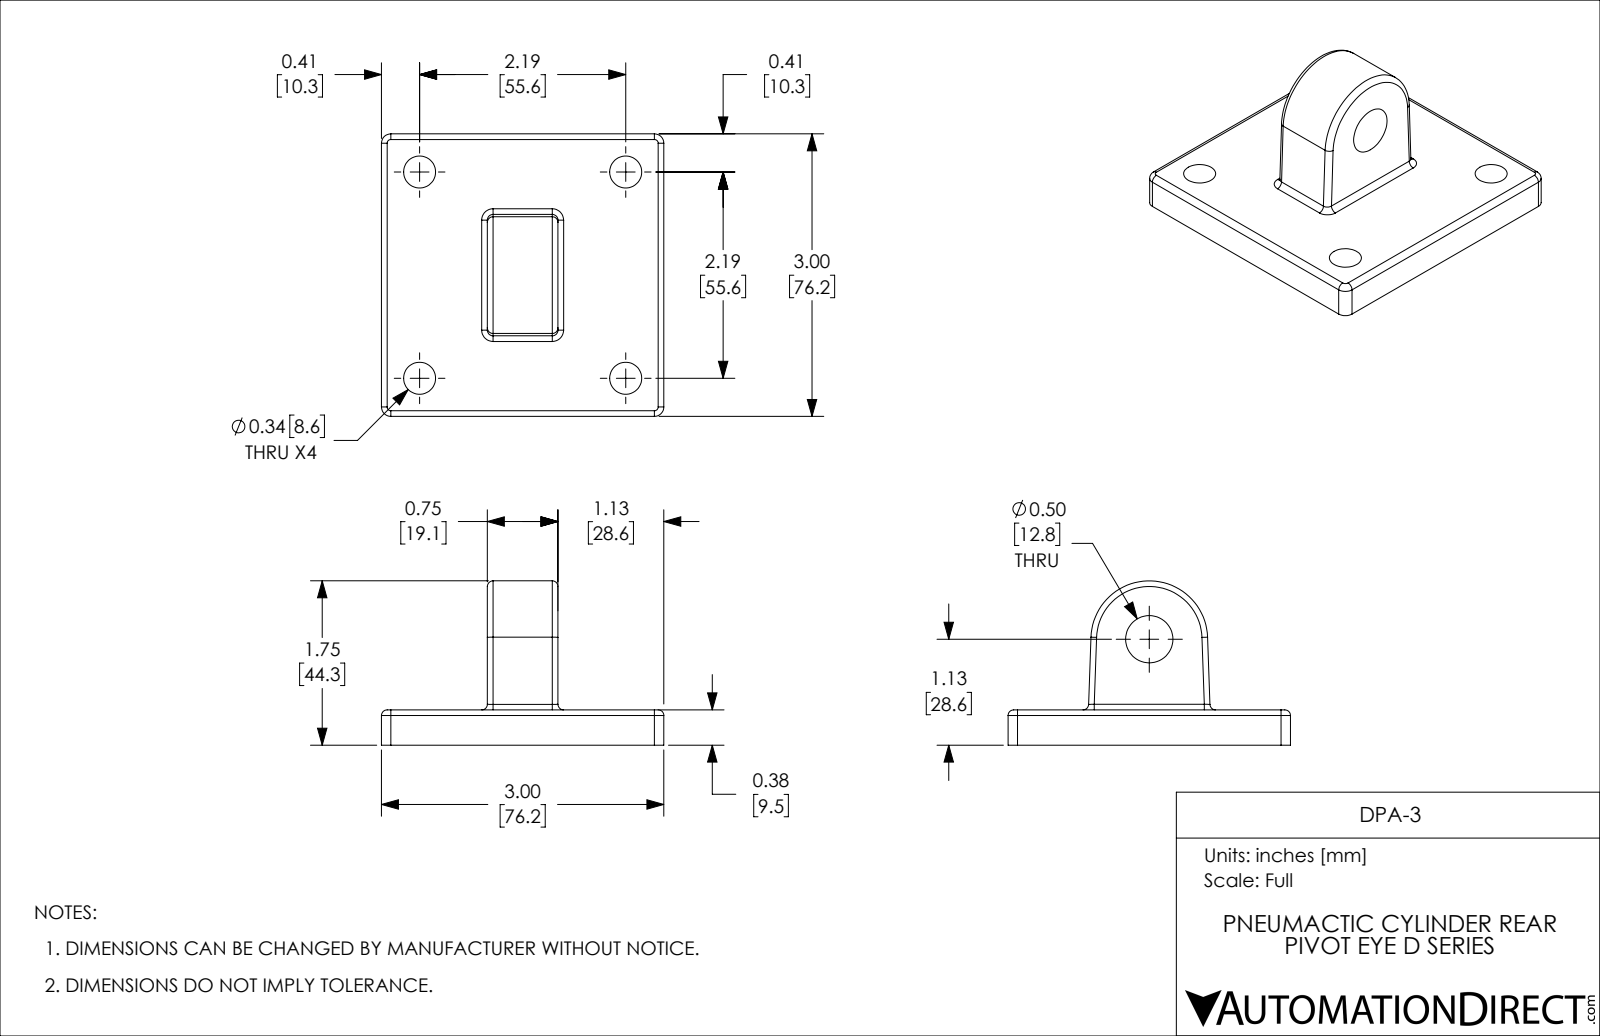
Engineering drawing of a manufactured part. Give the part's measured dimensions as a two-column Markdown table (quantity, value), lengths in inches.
| quantity | value |
| --- | --- |
| part name | DPA-3 |
| STEP written by | SolidWorks 2018 (AUTOMOTIVE_DESIGN) |
| units | inches |
| bodies | 1 solid, 48 faces (10 planar, 28 cylindrical, 10 other) |
| overall size | 3 × 3 × 1.745 |
| volume | 4.241 in³ |
| surface area | 28.23 in² |
| round holes (diameter × count) | 0.34 × 4, 0.502 × 1 |
| partial cylindrical surfaces (radius × count) | 0.06 × 12, 0.1 × 4, 0.62 × 1 |
| main face-to-face distances | 0.375, 1.125, 1.875, 3, 0.75 |
| hole center spacings | 2.19, 3.097 |
